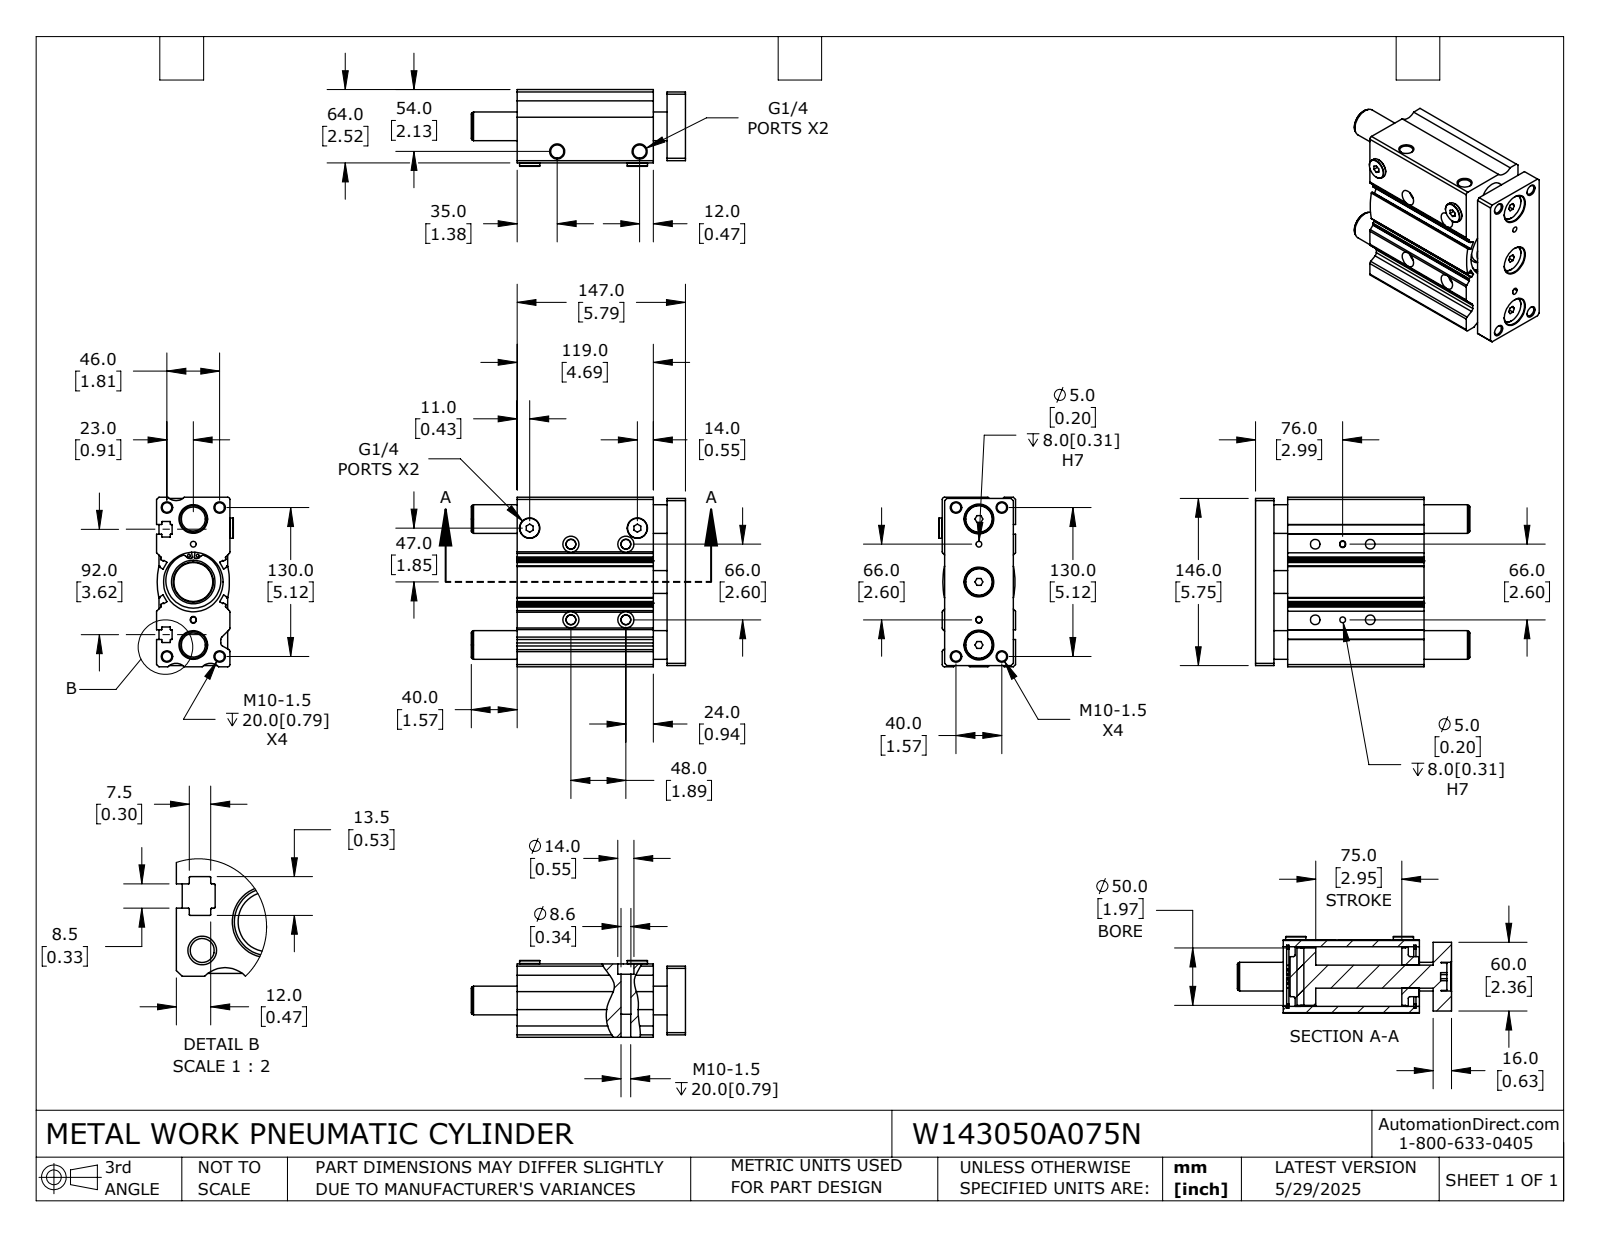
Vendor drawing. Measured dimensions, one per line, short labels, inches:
name: W143050A075N_BODY; W143050A075N_ROD; W143050A075N
written by: SolidWorks 2024 (CONFIG_CONTROL_DESIGN)
unit: in
bodies: 6 solids, 466 faces (186 planar, 224 cylindrical, 56 other)
size: 7.362 × 5.827 × 2.638
volume: 63.26 in³; area: 326.9 in²
holes: 12× ⌀0.33, 4× ⌀0.098, 4× ⌀0.197, 4× ⌀0.339, 4× ⌀0.551, 3× ⌀0.984, 2× ⌀0.451, 2× ⌀1.89, 1× ⌀0.787
bosses: 3× ⌀0.945, 2× ⌀0.697, 1× ⌀2.165, 1× ⌀2.047, 1× ⌀1.969, 1× ⌀1.378
rounds: 44× R0.012, 12× R0.02, 10× R0.118, 6× R0.079, 6× R2.677, 4× R0.039, 4× R0.098, 3× R0.394
face distances: 0.472, 2.52, 4.685, 0.63, 5.787, 5.157, 0.079, 1.102, 2.441, 0.236
hole spacings: 0.118, 0.424, 0.869, 0.88, 0.916, 0.945, 0.963, 0.987
